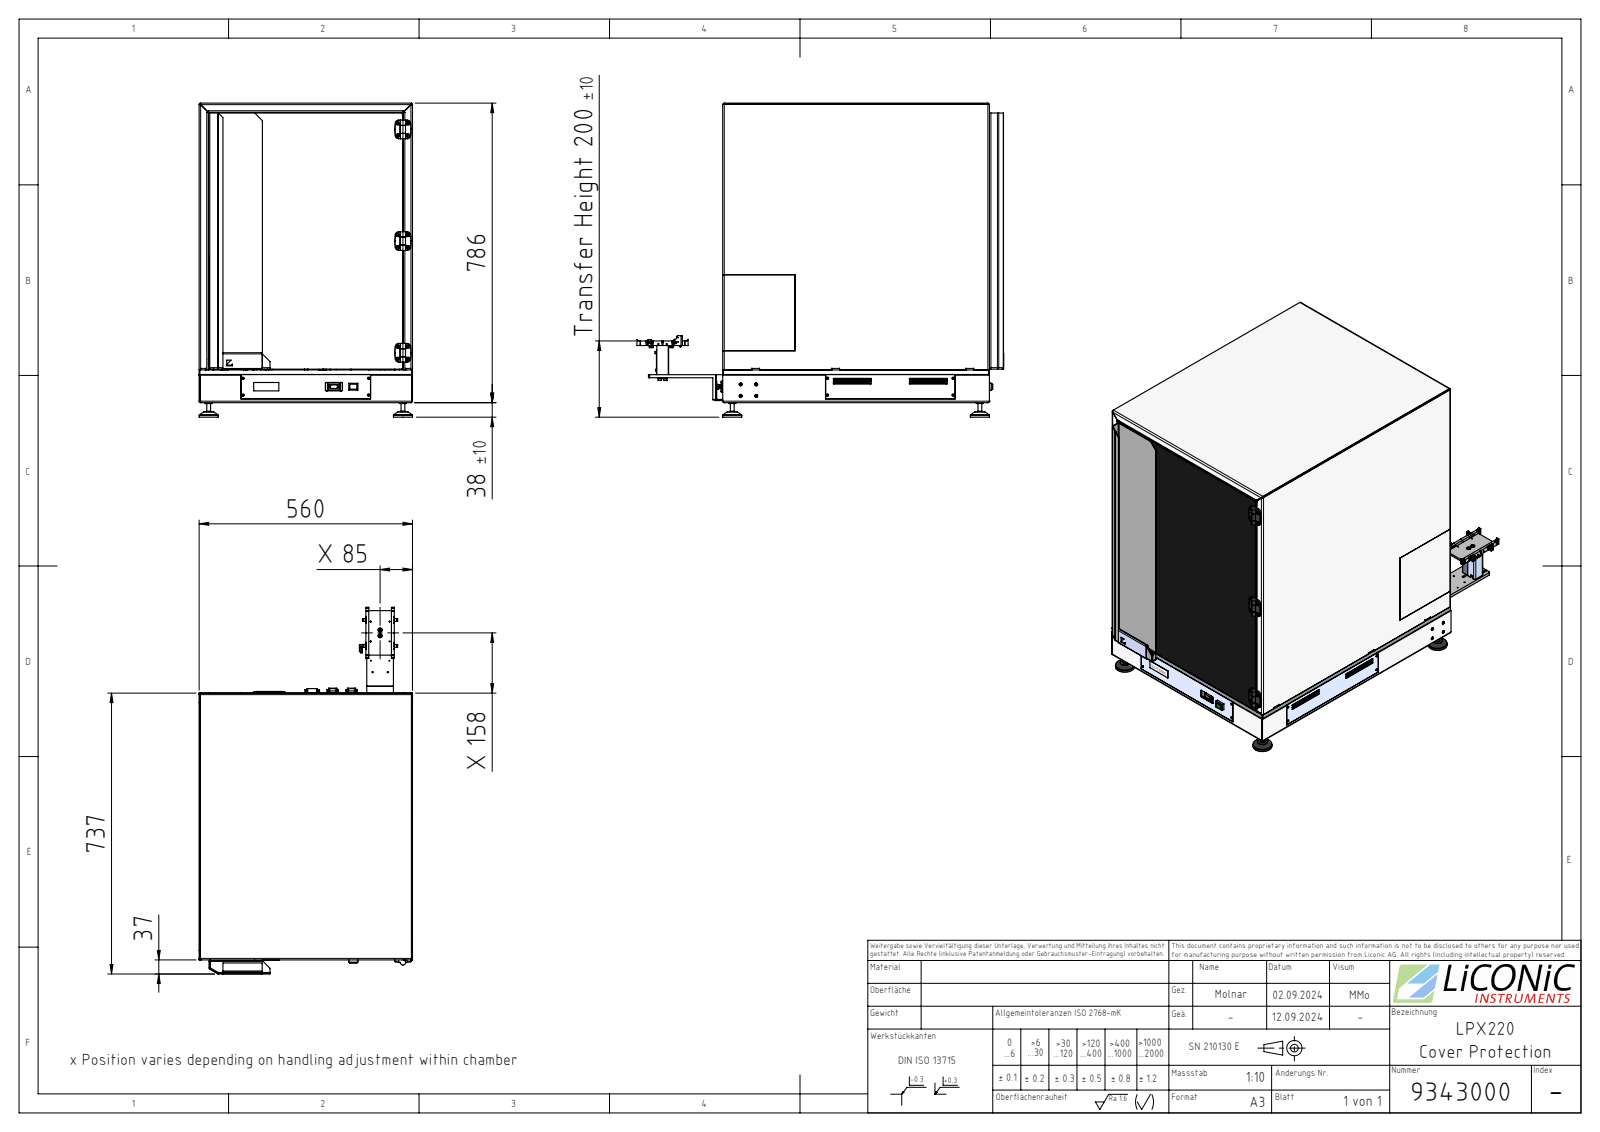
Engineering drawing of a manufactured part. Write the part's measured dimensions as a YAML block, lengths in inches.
part_name: "9343000"
step_written_by: "SolidWorks 2022 (AUTOMOTIVE_DESIGN)"
units: inches
bodies: {solids: 50, faces: 7802, planar: 4336, cylindrical: 3290, other: 176}
overall_size: [37.901, 32.441, 22.048]
volume: 883.6
surface_area: 12310
round_holes:
  - {diameter: 0.098, count: 63}
  - {diameter: 0.165, count: 55}
  - {diameter: 0.13, count: 33}
  - {diameter: 0.256, count: 32}
  - {diameter: 0.157, count: 22}
  - {diameter: 0.28, count: 16}
  - {diameter: 0.134, count: 14}
  - {diameter: 0.177, count: 14}
  - {diameter: 0.354, count: 12}
  - {diameter: 0.244, count: 11}
  - {diameter: 0.236, count: 10}
  - {diameter: 0.122, count: 8}
round_bosses_or_shafts:
  - {diameter: 0.157, count: 6}
  - {diameter: 1.969, count: 4}
  - {diameter: 0.394, count: 4}
  - {diameter: 0.059, count: 3}
  - {diameter: 21.26, count: 1}
  - {diameter: 9.213, count: 1}
  - {diameter: 0.61, count: 1}
  - {diameter: 0.571, count: 1}
partial_cylinders:
  - {radius: 0.004, count: 832}
  - {radius: 0.01, count: 832}
  - {radius: 0.079, count: 213}
  - {radius: 0.197, count: 121}
  - {radius: 0.098, count: 114}
  - {radius: 0.039, count: 71}
  - {radius: 0.118, count: 38}
  - {radius: 0.157, count: 36}
face_to_face_distances: [0.079, 21.969, 27.559, 27.48, 30.866, 22.047, 21.89, 28.031, 2.835, 0.197]
hole_center_spacings: [1.614, 1.181, 2, 6.236, 3.375, 8.148, 10.645, 17.224]
